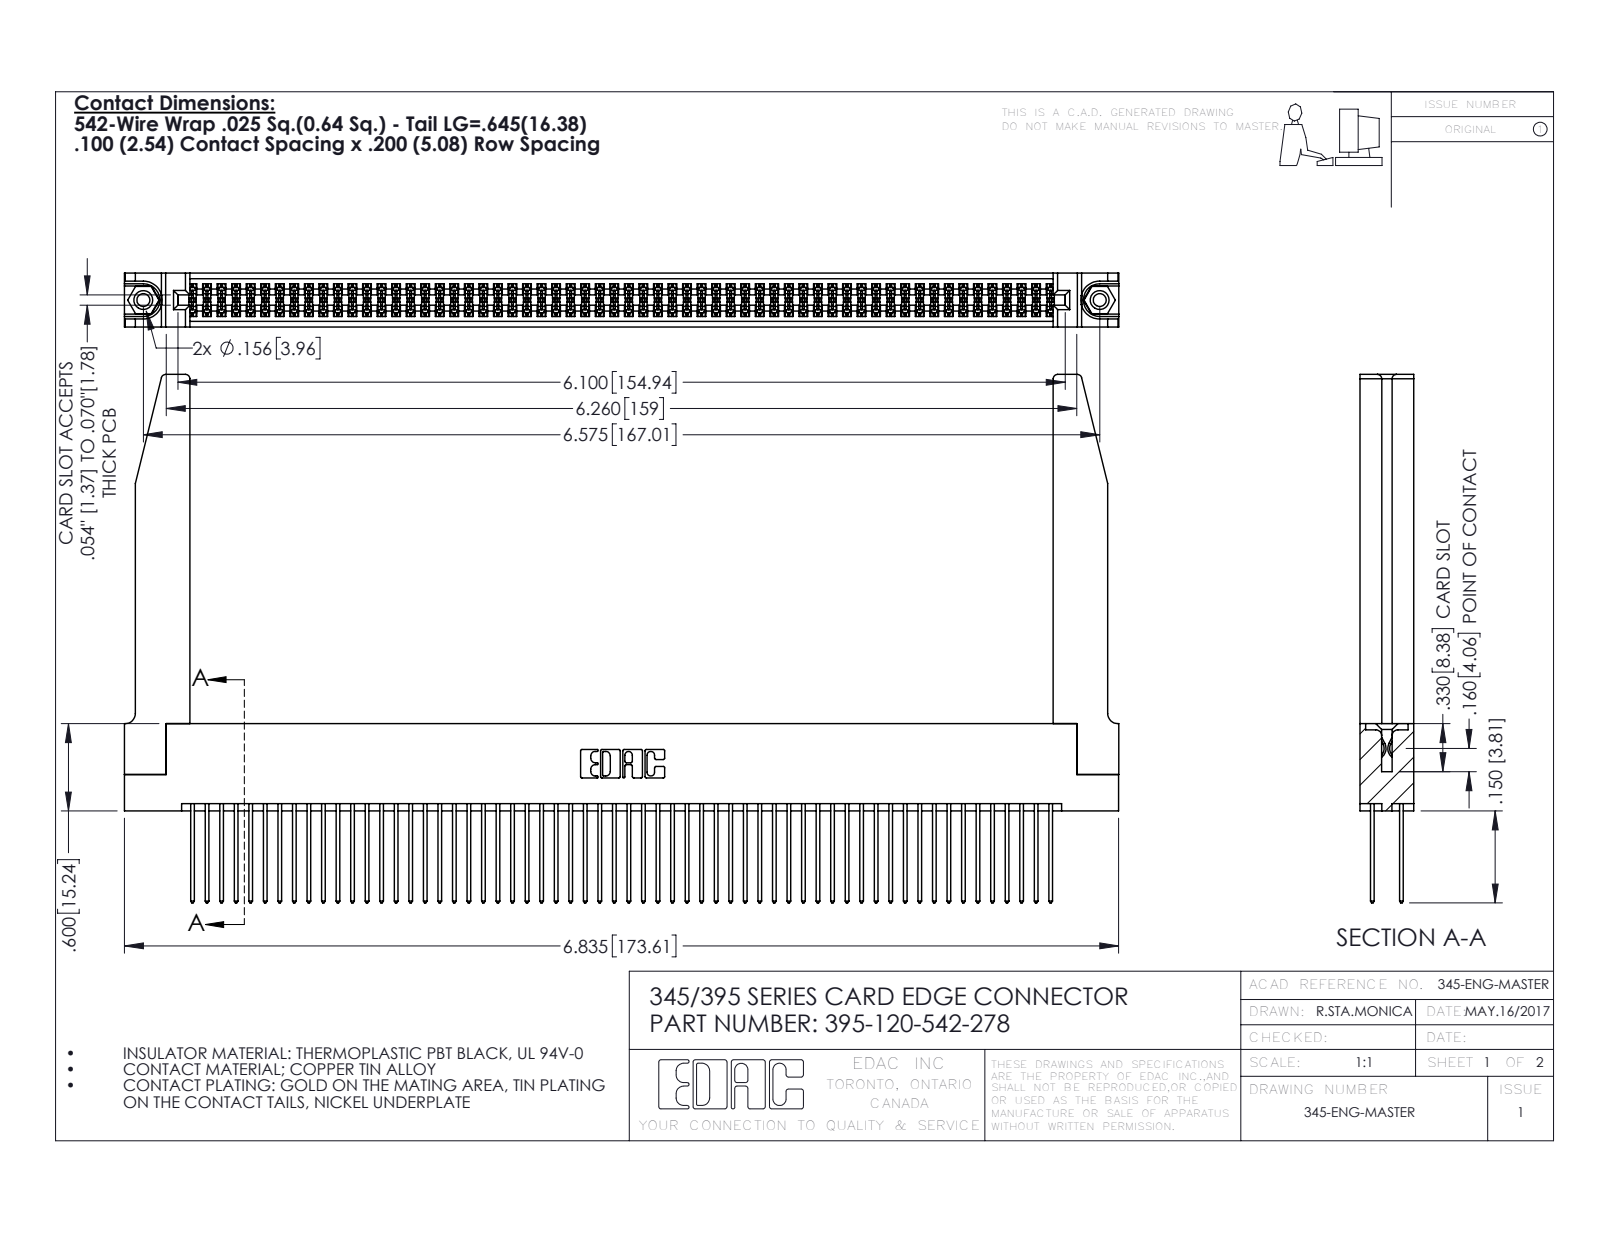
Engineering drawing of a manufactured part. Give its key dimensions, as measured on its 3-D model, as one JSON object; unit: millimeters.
{"part_name": "345-292-001_345-293-142; 345-220-078_345-220-078; 345 Part_Flush Mounting Lugs - 0.156 Dia-TH; 345-250-001_345-250-001-102 (+1 more)", "step_written_by": "SolidWorks 2016 (CONFIG_CONTROL_DESIGN)", "units": "millimeters", "bodies": {"solids": 125, "faces": 6360, "planar": 4182, "cylindrical": 2126, "other": 52}, "overall_size": [173.6, 92.3, 9.4], "volume_mm3": 25370, "surface_area_mm2": 35810, "round_holes": [[2.3, 2], [3.2, 2], [4, 2], [1.6, 1]], "round_bosses_or_shafts": [[3.9, 2]], "partial_cylinders_radius": [[0.2, 180], [0.3, 120], [0.3, 22], [0.8, 8], [0.2, 6], [0.8, 6], [0.7, 3], [0.4, 2]], "face_to_face_distances": [1.8, 7.6, 9.4, 5.1, 2.5, 6.9, 0.6, 5.7, 4.4, 3.8], "hole_center_spacings": [6.9, 161, 167]}
